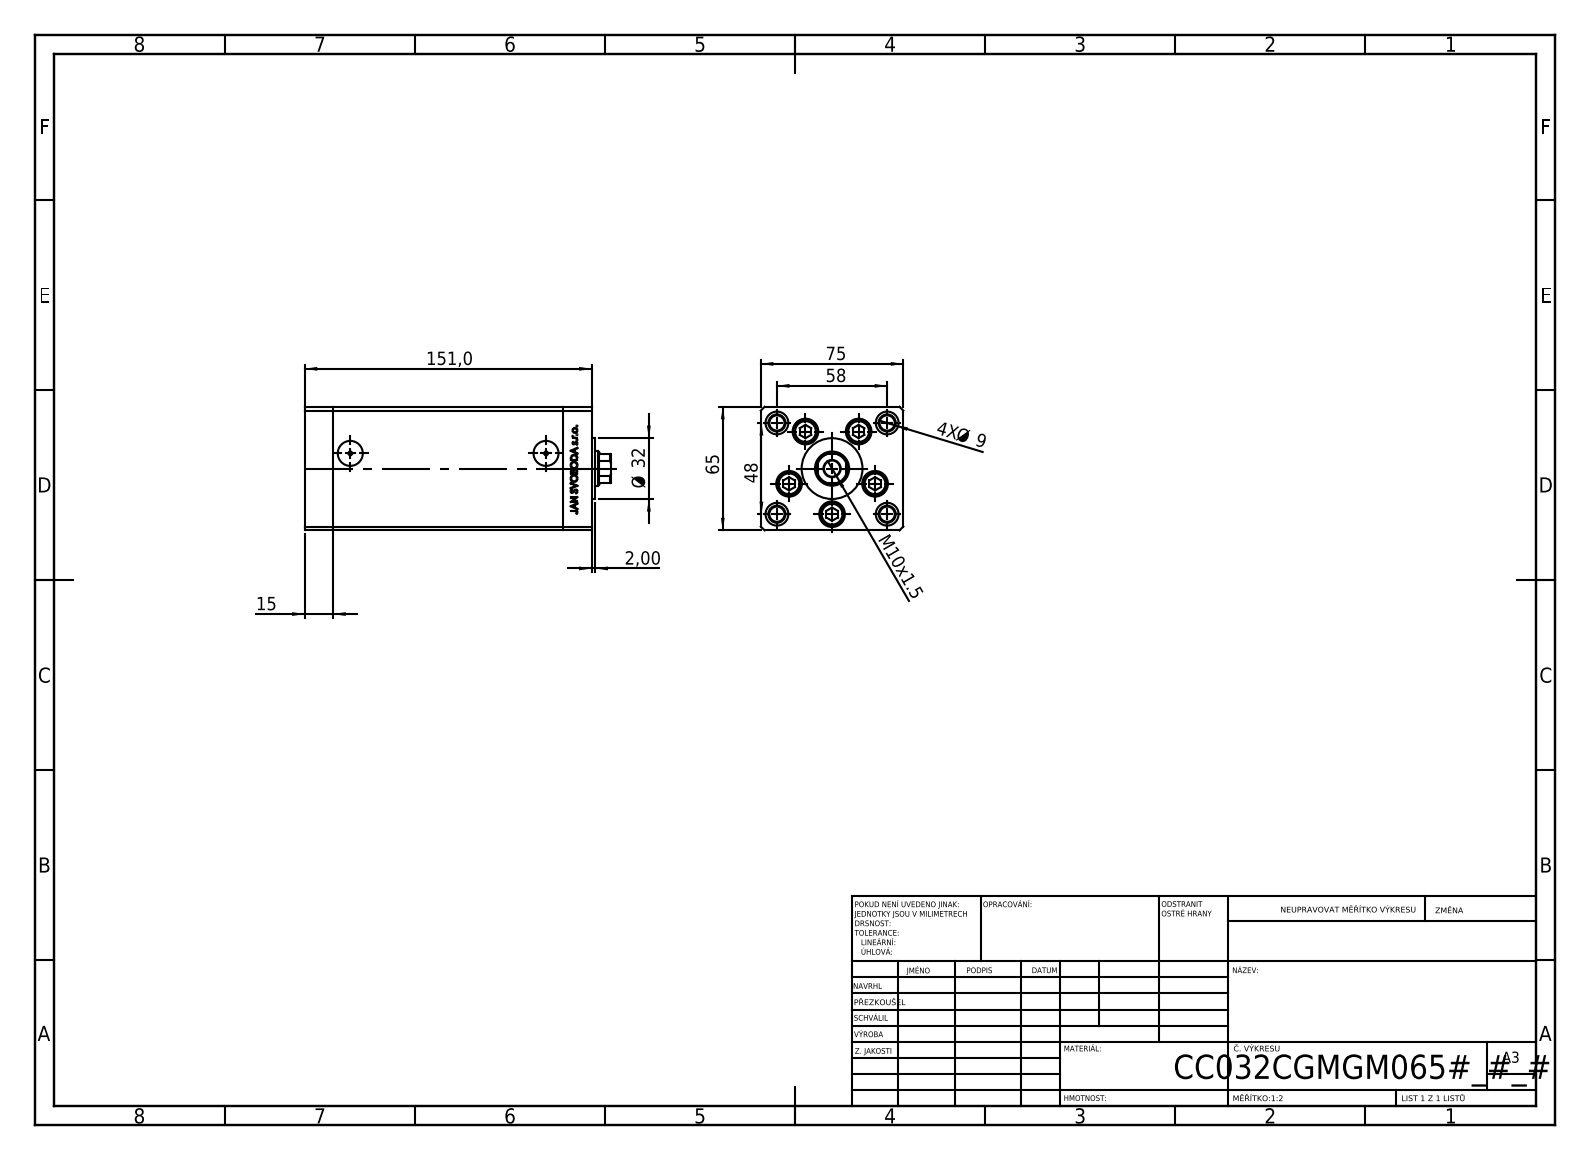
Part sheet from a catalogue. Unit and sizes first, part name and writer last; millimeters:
Units: millimetres
Overall size (bounding box): 161 × 75 × 65
Round holes (diameter × count): ⌀9 ×9, ⌀13.5 ×5, ⌀8 ×4, ⌀12 ×4, ⌀2 ×2, ⌀13.16 ×2, ⌀8.5 ×1, ⌀12.5 ×1, ⌀18 ×1
Round bosses / shafts (diameter × count): ⌀8 ×5, ⌀12.5 ×4, ⌀32 ×1
Partial cylindrical surfaces — rounded edges, fillets, slot ends (radius × count): R0.93 ×2, R8.5 ×1
Main face-to-face distances: 75, 65, 15, 121, 136, 151, 28, 127, 13, 9
Hole centre spacings: 24, 37.64, 15.67, 17.22, 27.71, 28.83, 29, 32.63
Volume: 622 456 mm³ · Surface area: 133 970 mm²
Bodies: 13 solids, 1169 faces (540 planar, 167 cylindrical, 462 other)
Part name (STEP PRODUCT): ALLEN BOLT; V220C FRONT; V220C BACK_C; V220C_C MIDDLE (+1 more)
STEP written by: SolidWorks 2019 (CONFIG_CONTROL_DESIGN)
